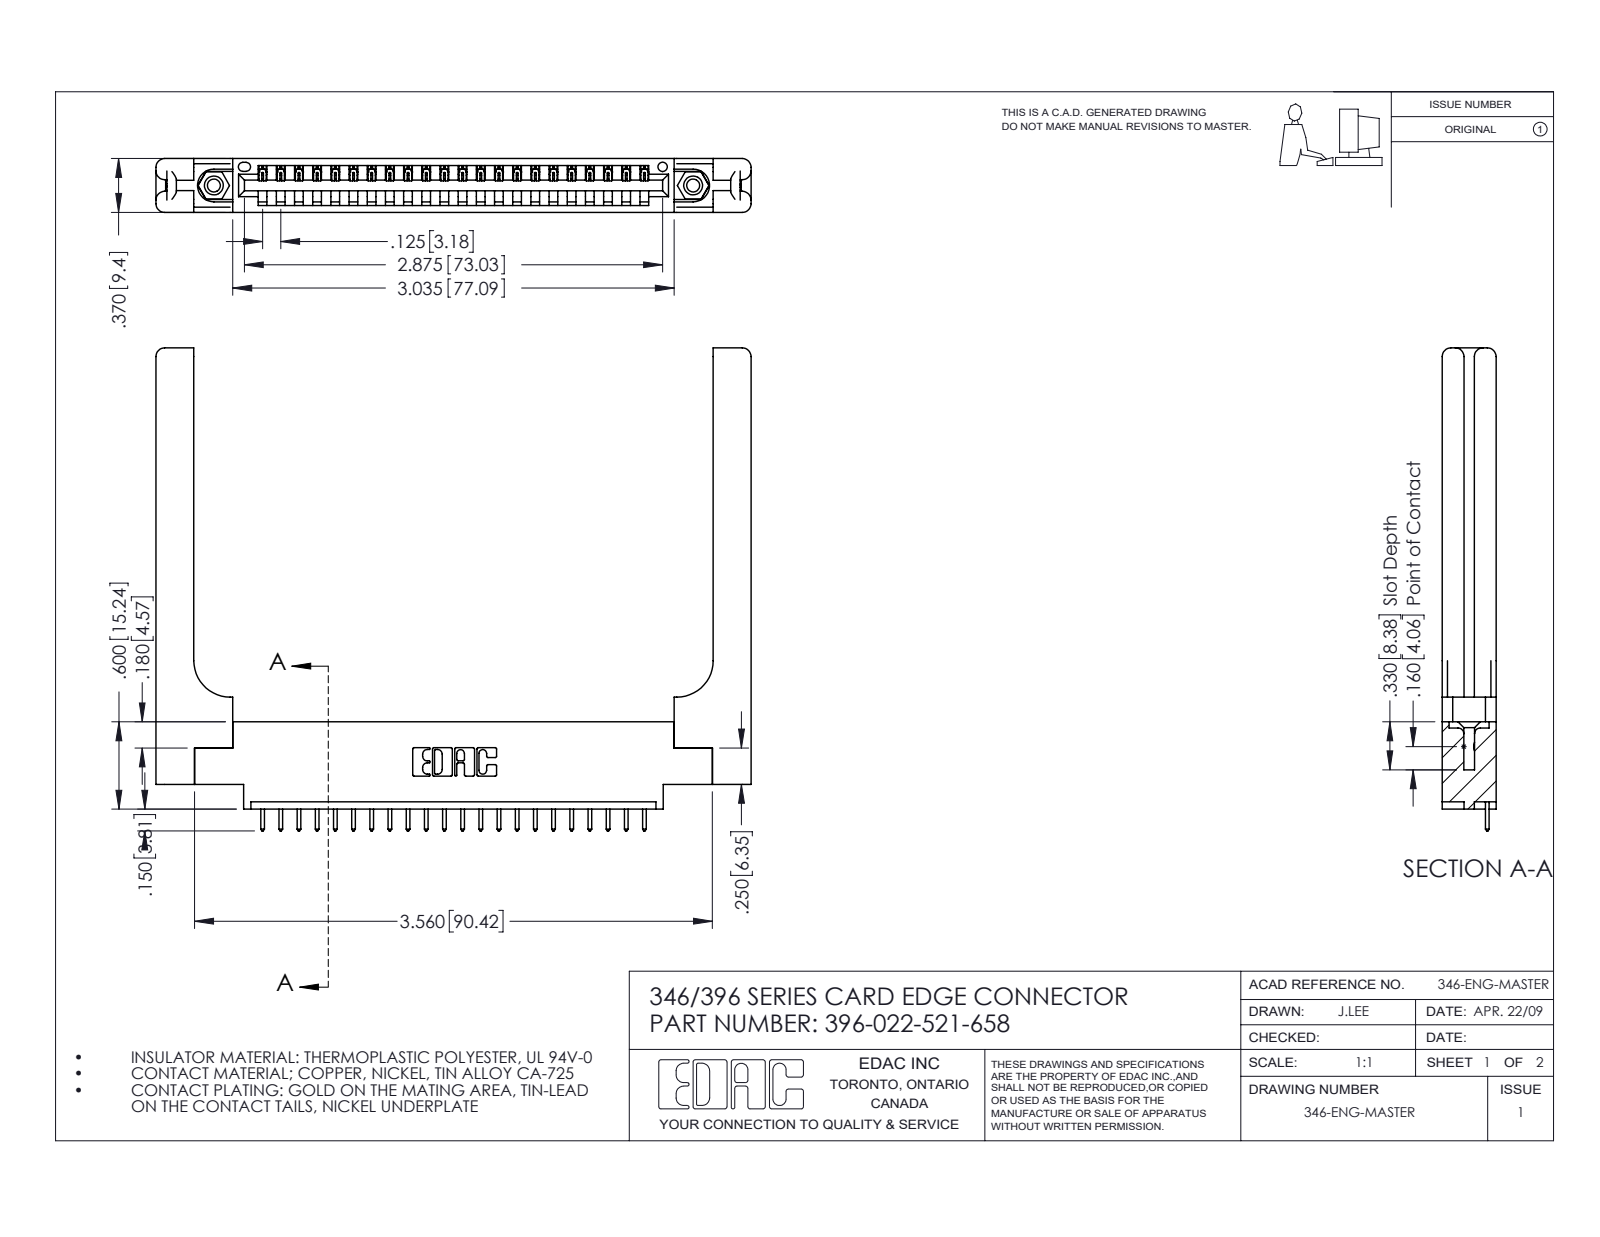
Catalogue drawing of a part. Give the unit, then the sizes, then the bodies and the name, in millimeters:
Units: millimetres
Overall size (bounding box): 103.9 × 84.3 × 9.4
Round holes (diameter × count): ⌀2.3 ×2, ⌀3.2 ×2, ⌀4 ×2, ⌀1.6 ×1
Round bosses / shafts (diameter × count): ⌀3.9 ×2
Partial cylindrical surfaces — rounded edges, fillets, slot ends (radius × count): R0.2 ×44, R0.3 ×44, R0.3 ×22, R1.5 ×16, R0.2 ×6, R0.8 ×6, R0.7 ×3, R0.8 ×2
Main face-to-face distances: 9.4, 1.8, 3.8, 3.8, 1.2, 8.2, 6.4, 7.6, 0.6, 2.6
Hole centre spacings: 6.2, 78.4, 83.7
Volume: 17 110 mm³ · Surface area: 16 850 mm²
Bodies: 27 solids, 1658 faces (1108 planar, 490 cylindrical, 60 other)
Part name (STEP PRODUCT): 396-022-521-658; 345-292-001_345-293-121; 346-220-058_345-220-058; 345-250-001_345-250-001-102 (+1 more)
STEP written by: SolidWorks 2016 (CONFIG_CONTROL_DESIGN)
